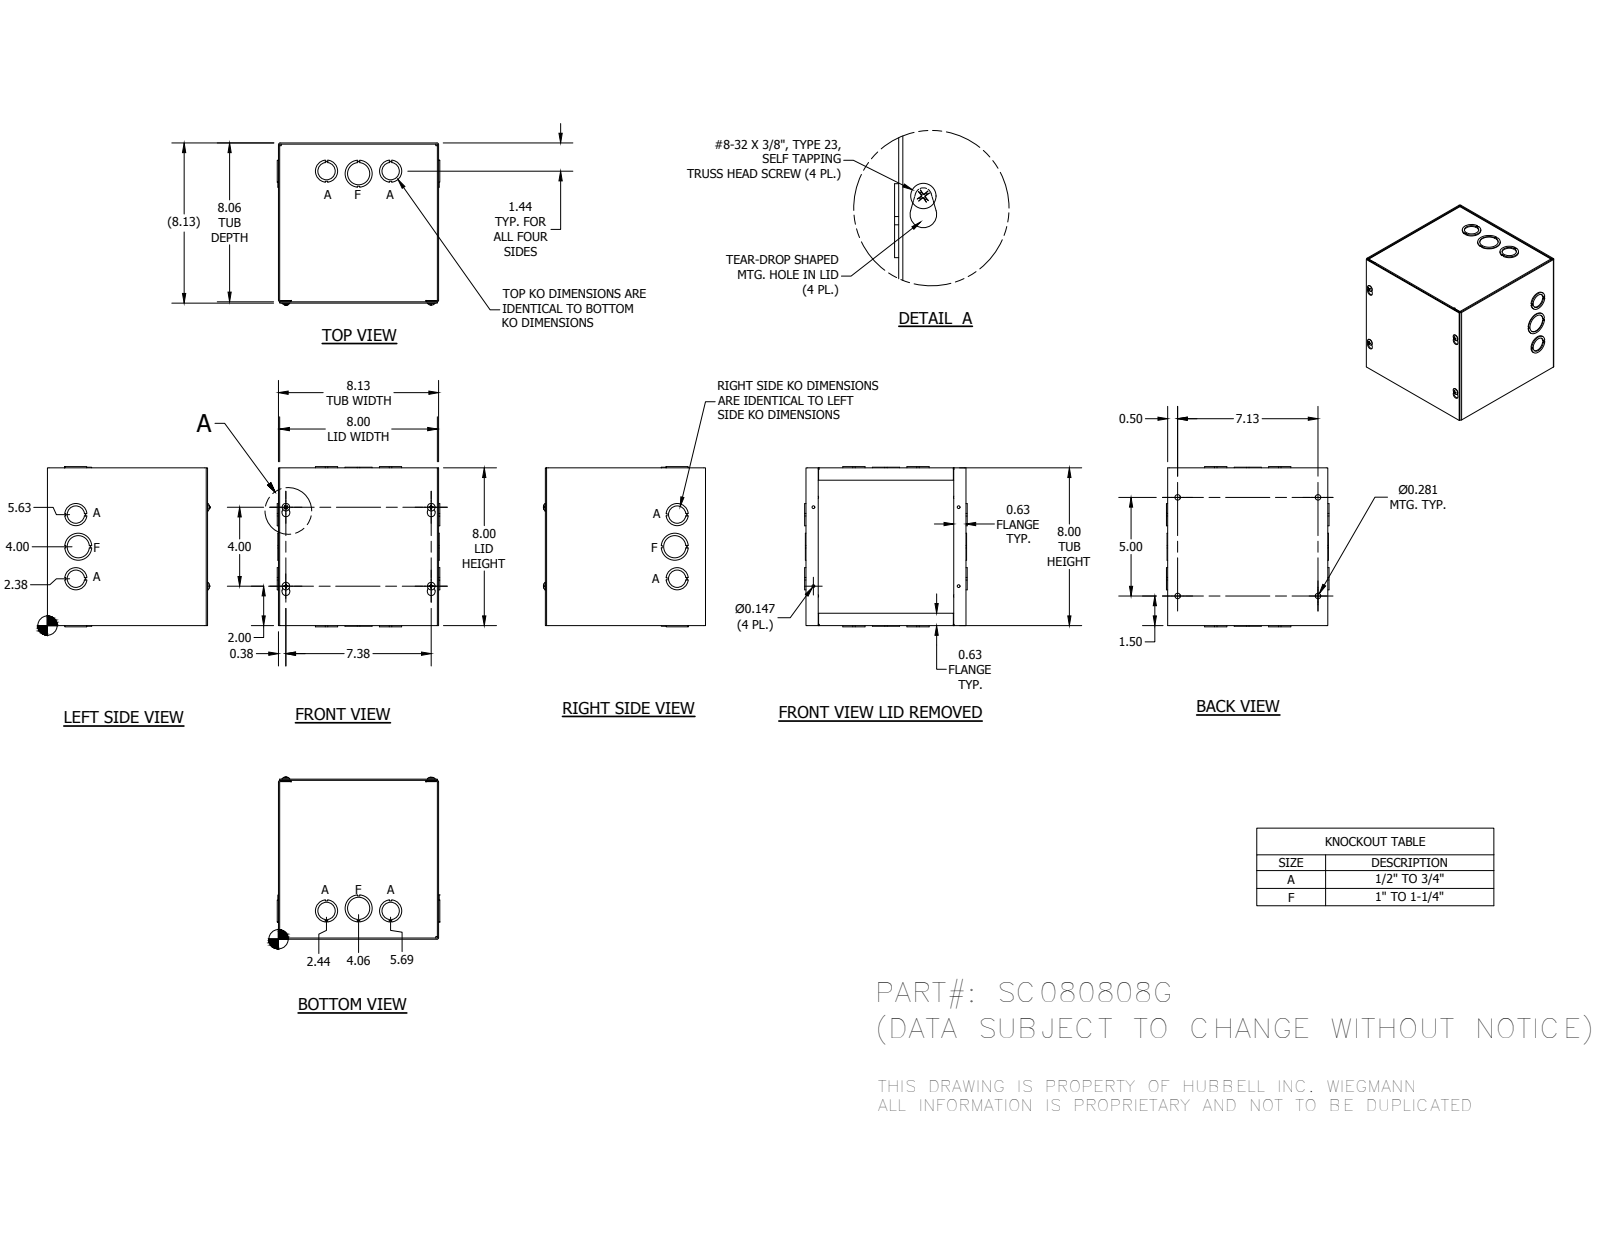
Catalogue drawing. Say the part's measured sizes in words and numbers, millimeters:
The part is named "SC080808GBLR; SC0808GTB; SC0808GLPA; 34056 (+1 more)". Its 3-D file was written by "Autodesk Inventor 2014 (AUTOMOTIVE_DESIGN)". It is 23 solids with 605 faces: 417 planar, 120 cylindrical and 68 other. Overall it measures 209.55 by 208.92 by 206.38 millimeters. Round holes: 8 of diameter 28.57, 6 of diameter 22.22, 4 of diameter 3.73, 4 of diameter 7.14, 2 of diameter 34.92. Round bosses or shafts: 4 of diameter 9.75, 4 of diameter 4.17. Partial cylindrical surfaces (rounded edges, fillets, slot ends): 12 of radius 0.4, 12 of radius 1.98, 4 of radius 3.17, 4 of radius 5.16. The main face-to-face distances are 1.59, 203.2, 204.79, 201.61, 200.02, 1.58, 204.78, 206.37, 206.38, 3.18. The hole center spacings are 13.09, 41.4, 114.34, 184.59, 216.74, 41.39, 82.55, 82.56.
